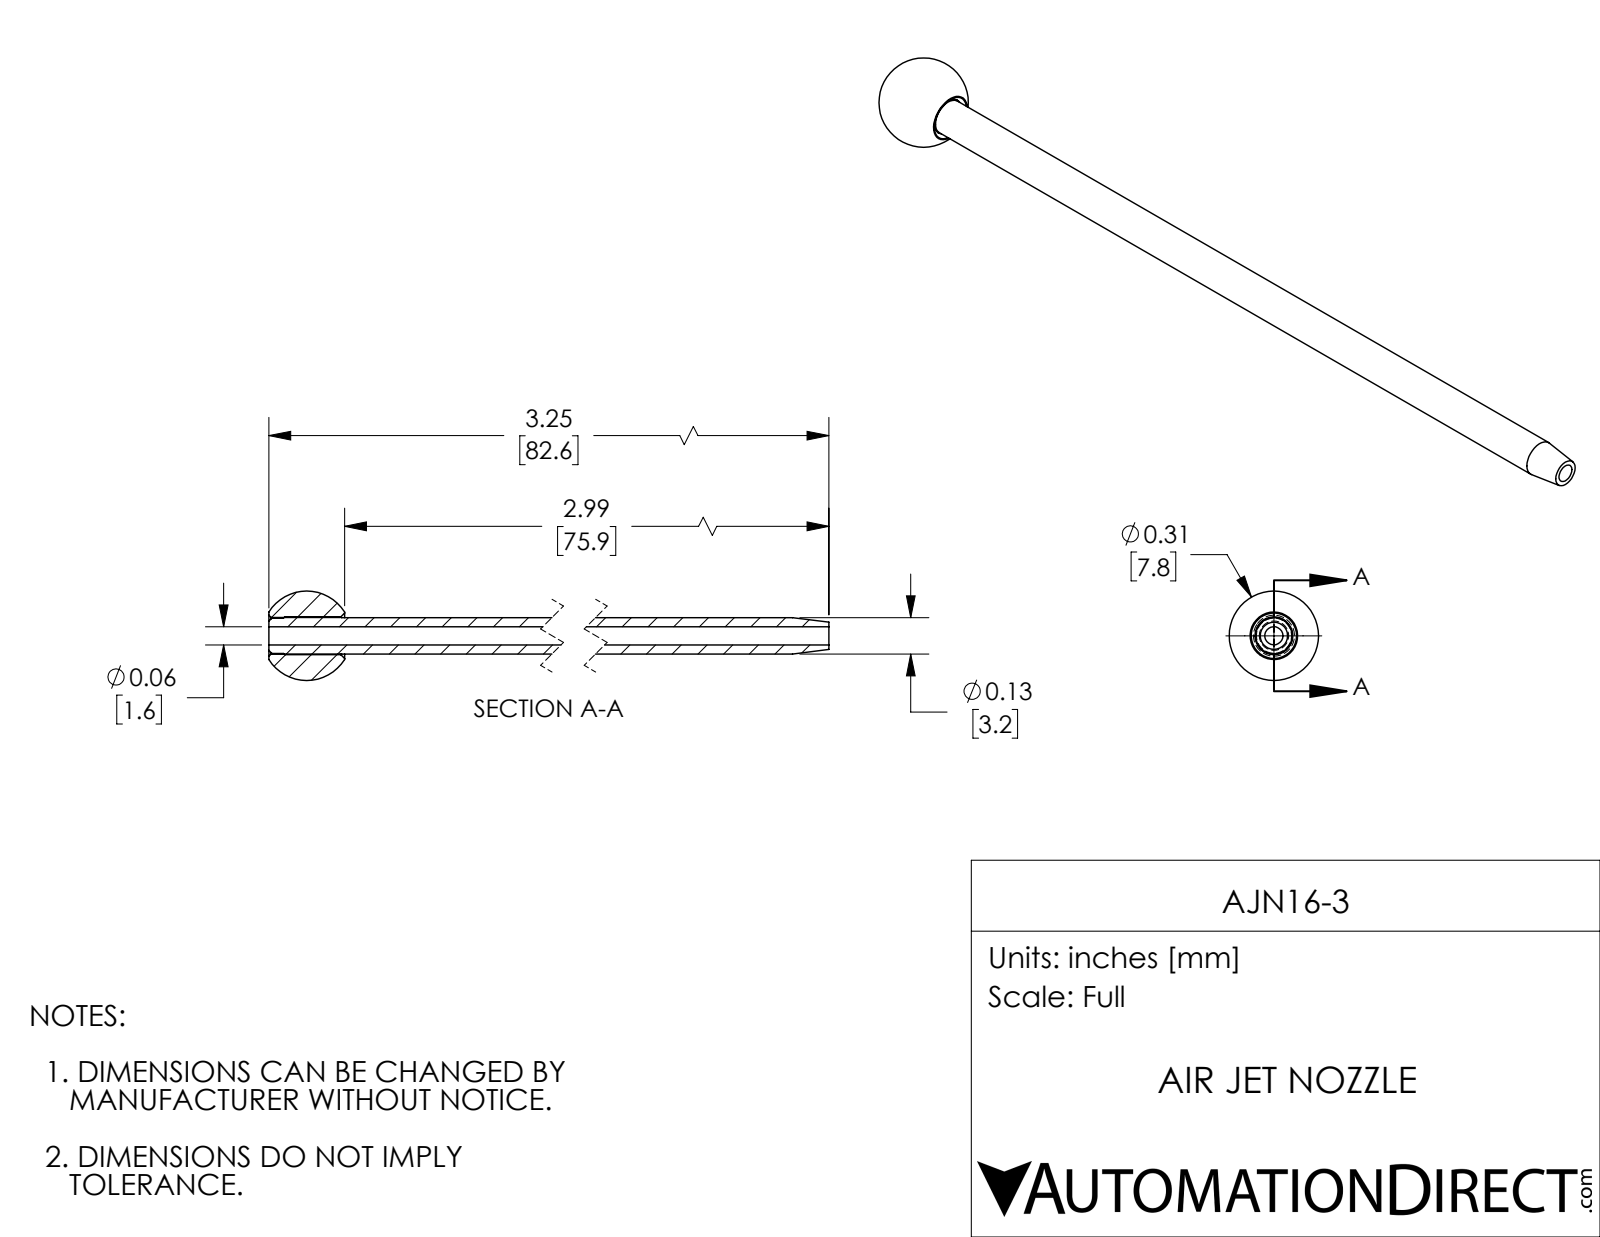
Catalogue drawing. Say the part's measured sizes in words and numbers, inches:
The part is named "AJN16-3". Its 3-D file was written by "SolidWorks 2018 (AUTOMOTIVE_DESIGN)". It is 2 solids with 28 faces: 4 planar, 10 cylindrical and 14 other. Overall it measures 3.25 by 0.307 by 0.307 inches. Its volume is 0.041 cubic inches and its surface area 2.288 square inches. Round holes: 1 of diameter 0.063, 1 of diameter 0.126. Round bosses or shafts: 1 of diameter 0.13, 1 of diameter 0.125, 1 of diameter 0.121. The main face-to-face distances are 3.25, 0.26, 2.99.
